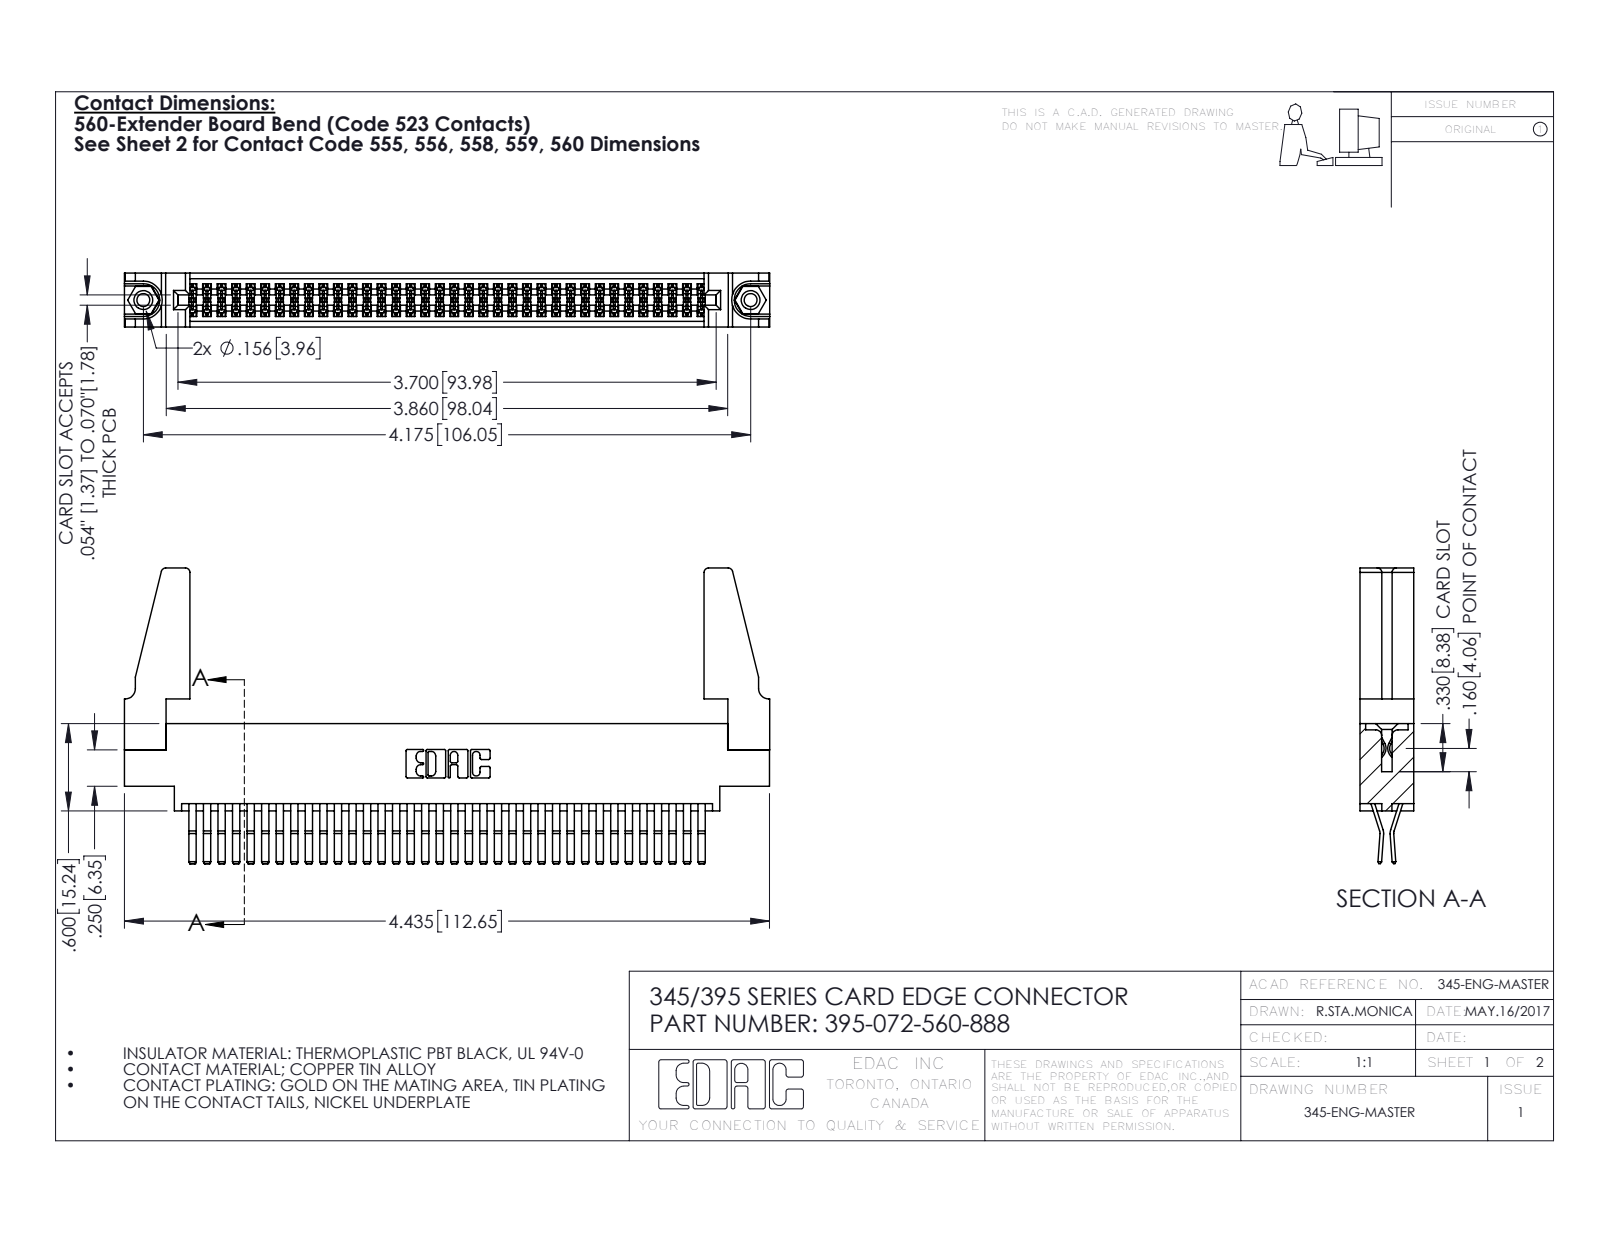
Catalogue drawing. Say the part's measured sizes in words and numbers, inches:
The part is named "395-072-560-888; 345-292-001_560 Tail; 345-250-001_345-250-001-102; 345-220-078_345-220-088 (+1 more)". Its 3-D file was written by "SolidWorks 2016 (CONFIG_CONTROL_DESIGN)". It is 77 solids with 3998 faces: 2532 planar, 1450 cylindrical and 16 other. Overall it measures 4.436 by 2.032 by 0.37 inches. Its volume is 0.885 cubic inches and its surface area 32.53 square inches. Round holes: 2 of diameter 0.089, 2 of diameter 0.125, 2 of diameter 0.156, 1 of diameter 0.064. Round bosses or shafts: 2 of diameter 0.155. Partial cylindrical surfaces (rounded edges, fillets, slot ends): 109 of radius 0.006, 22 of radius 0.01, 8 of radius 0.03, 6 of radius 0.007, 6 of radius 0.031, 3 of radius 0.026, 2 of radius 0.01, 2 of radius 0.014. The main face-to-face distances are 0.072, 0.298, 0.37, 0.025, 0.2, 0.098, 0.272, 0.225, 0.175, 0.149. The hole center spacings are 0.27, 3.939, 4.175.
